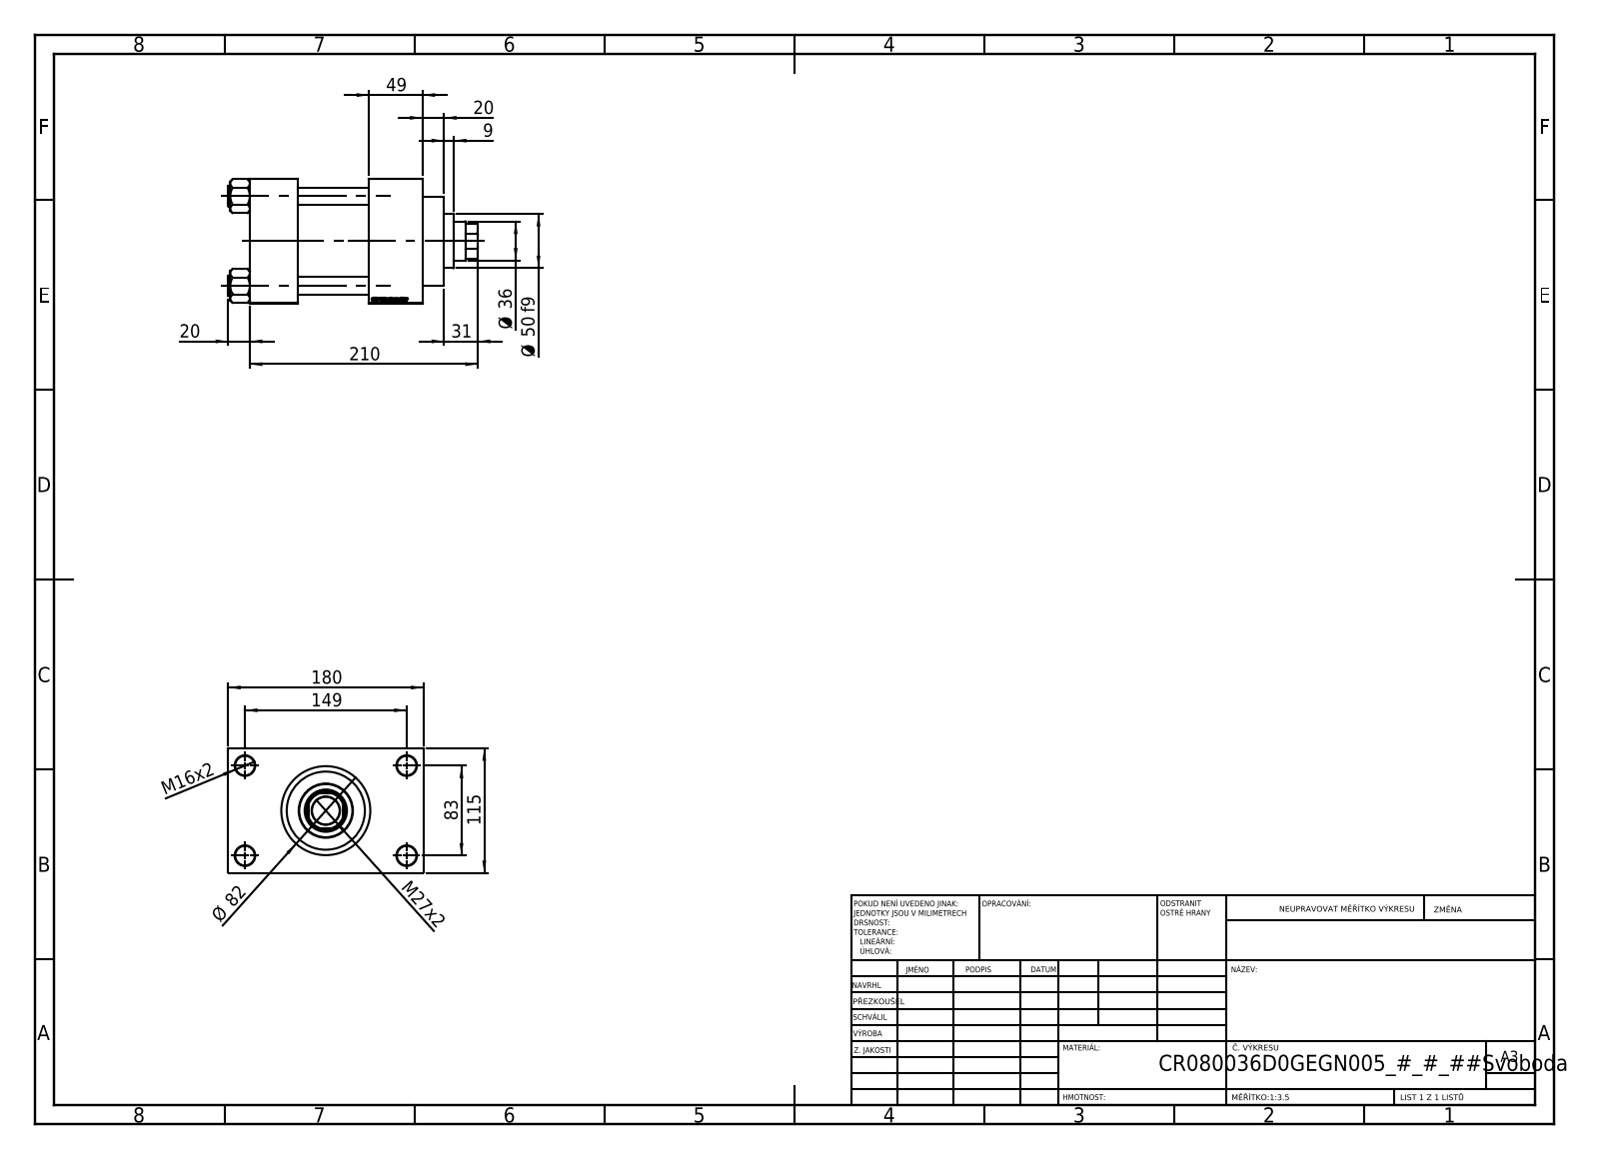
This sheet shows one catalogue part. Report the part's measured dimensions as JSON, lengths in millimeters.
{"part_name": "V215CR_VCP_D; V215_VC_A; V215CR_D_TYCINKA; V215CR_D_Body (+1 more)", "step_written_by": "SolidWorks 2019 (CONFIG_CONTROL_DESIGN)", "units": "millimeters", "bodies": {"solids": 11, "faces": 1152, "planar": 545, "cylindrical": 89, "other": 518}, "overall_size": [230, 180, 115], "volume_mm3": 1997000, "surface_area_mm2": 293897, "round_holes": [[16, 4], [18, 4], [7, 2], [26.44, 2], [35, 2], [25.5, 1], [36, 1], [39, 1], [61, 1], [72, 1], [80, 1]], "round_bosses_or_shafts": [[19, 4], [86, 1], [82, 1], [50, 1]], "partial_cylinders_radius": [[17.5, 1]], "face_to_face_distances": [115, 66, 110, 49, 44, 159, 32.5, 147.5, 20, 69], "hole_center_spacings": [33.15, 58.48, 82.7, 85.28, 89.24, 115.85, 142.43, 83]}
